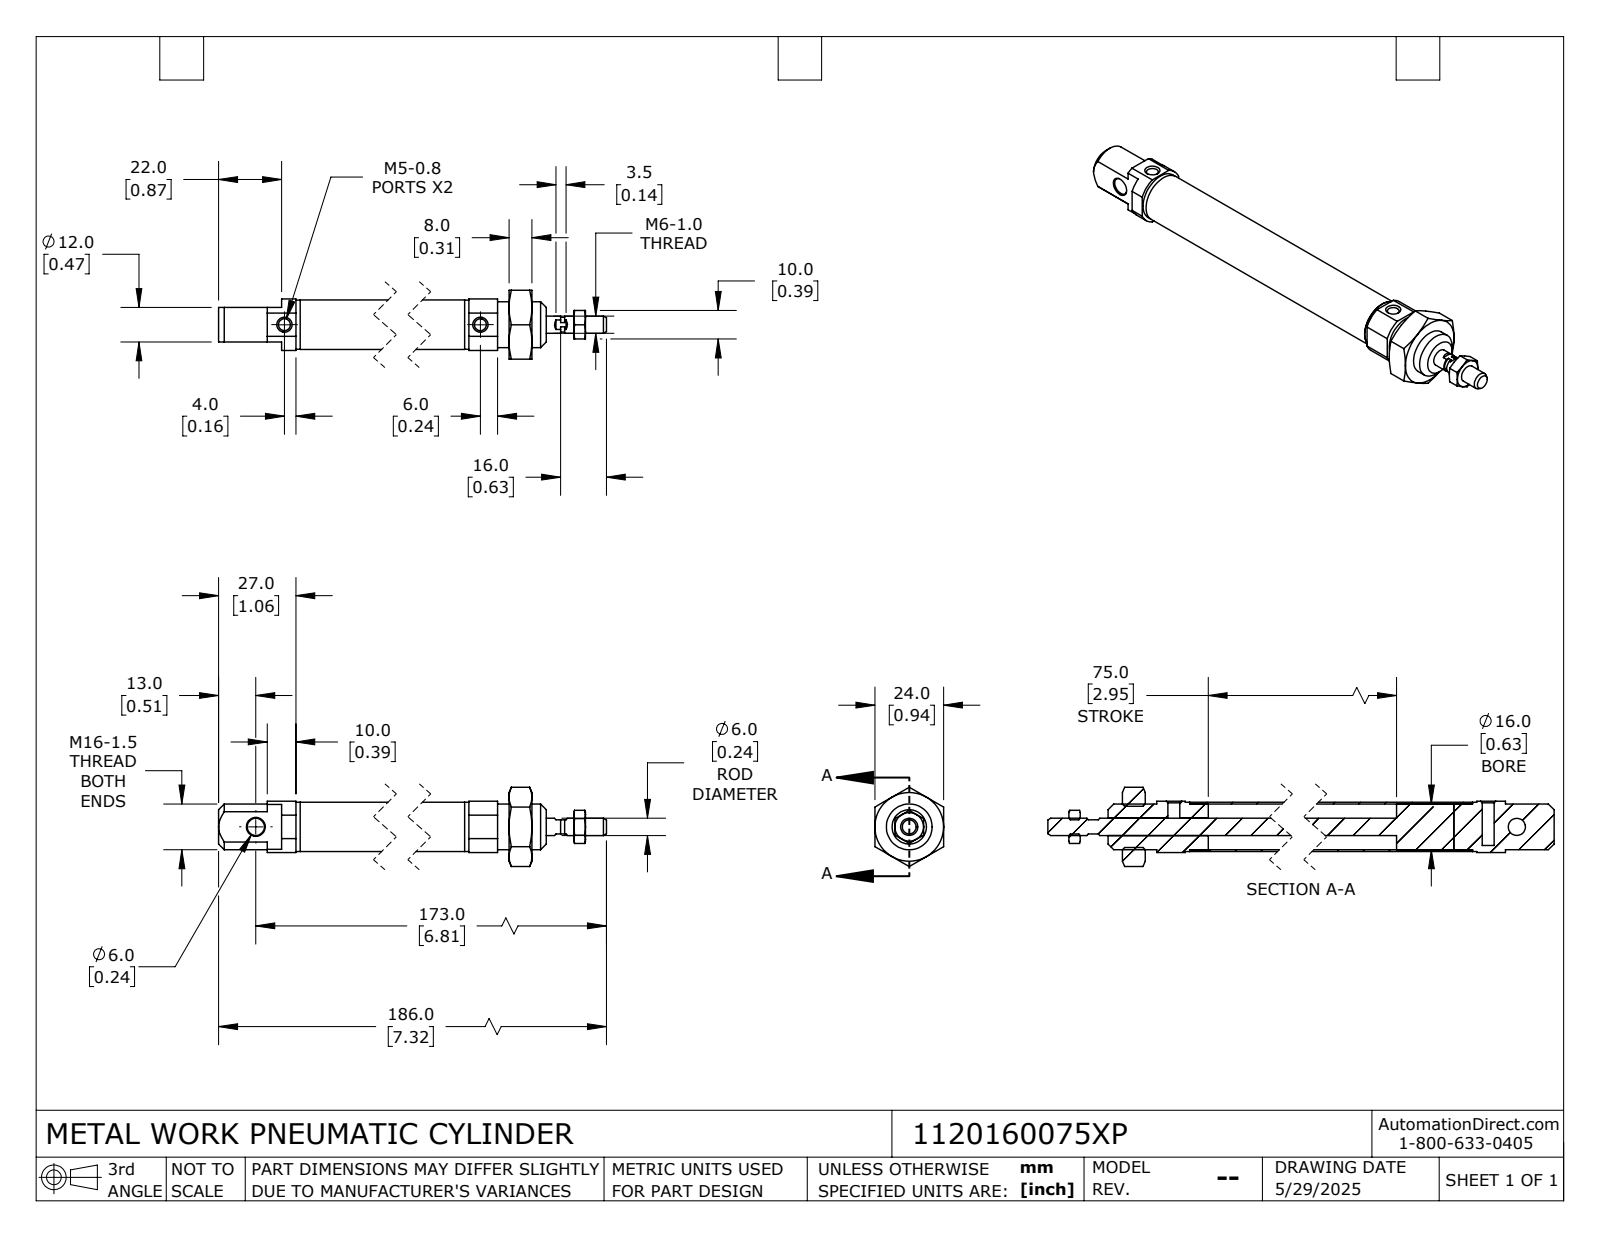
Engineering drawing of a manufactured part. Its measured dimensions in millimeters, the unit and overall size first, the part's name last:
Units: millimetres
Overall size (bounding box): 186 × 27.71 × 24
Round holes (diameter × count): ⌀4.13 ×2, ⌀4.92 ×1, ⌀6 ×1, ⌀14.38 ×1
Round bosses / shafts (diameter × count): ⌀17.27 ×1, ⌀17.2 ×1, ⌀16.15 ×1, ⌀16 ×1, ⌀6 ×1, ⌀5.2 ×1
Partial cylindrical surfaces — rounded edges, fillets, slot ends (radius × count): R9.85 ×1
Main face-to-face distances: 8, 18, 24, 22, 125, 12, 130, 17, 117, 2.97
Hole centre spacings: 119
Volume: 27 461 mm³ · Surface area: 22 914 mm²
Bodies: 6 solids, 146 faces (55 planar, 45 cylindrical, 46 other)
Part name (STEP PRODUCT): 1120160075XP_ROD; 1120160075XP_BODY; 1120160075XP
STEP written by: SolidWorks 2024 (CONFIG_CONTROL_DESIGN)
